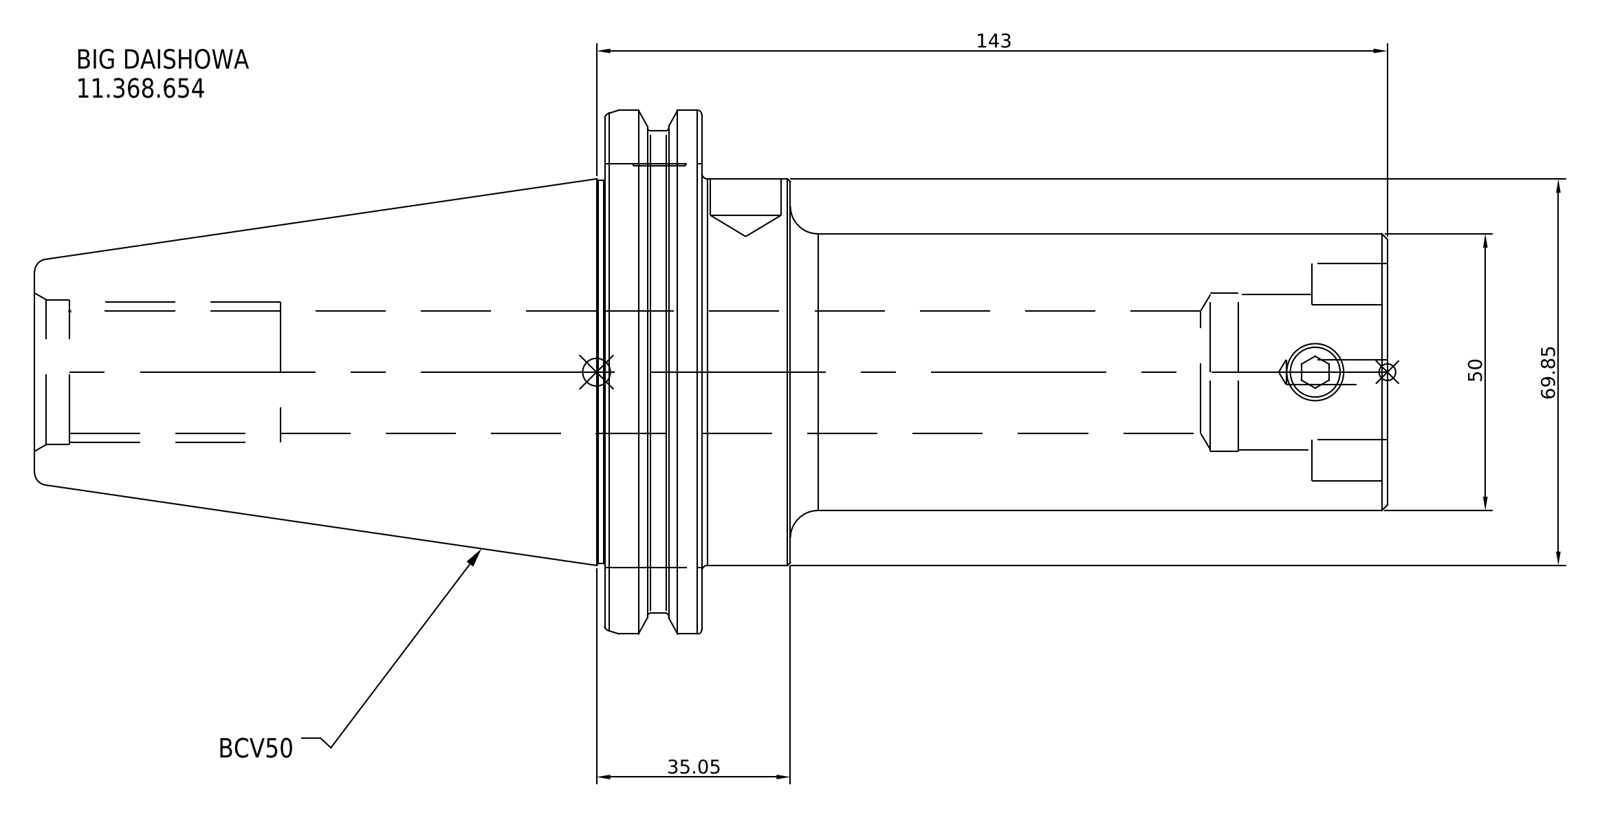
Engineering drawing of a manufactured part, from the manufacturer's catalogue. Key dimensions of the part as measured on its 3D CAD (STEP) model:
Part name (STEP PRODUCT): 11.368.654
STEP written by: SolidWorks 2021 (CONFIG_CONTROL_DESIGN)
Units: millimetres
Bodies: 1 solid, 16 faces (7 planar, 6 cylindrical, 3 other)
Overall size (bounding box): 244.6 × 98.43 × 98.43
Volume: 654 538 mm³ · Surface area: 57 938 mm²
Round bosses / shafts (diameter × count): ⌀98.43 ×1, ⌀91.29 ×1, ⌀69.85 ×1, ⌀50 ×1
Main face-to-face distances: 17.55, 123.95, 141.5, 108, 15.95, 33.5, 244.6, 136.6, 120.65, 103.1
